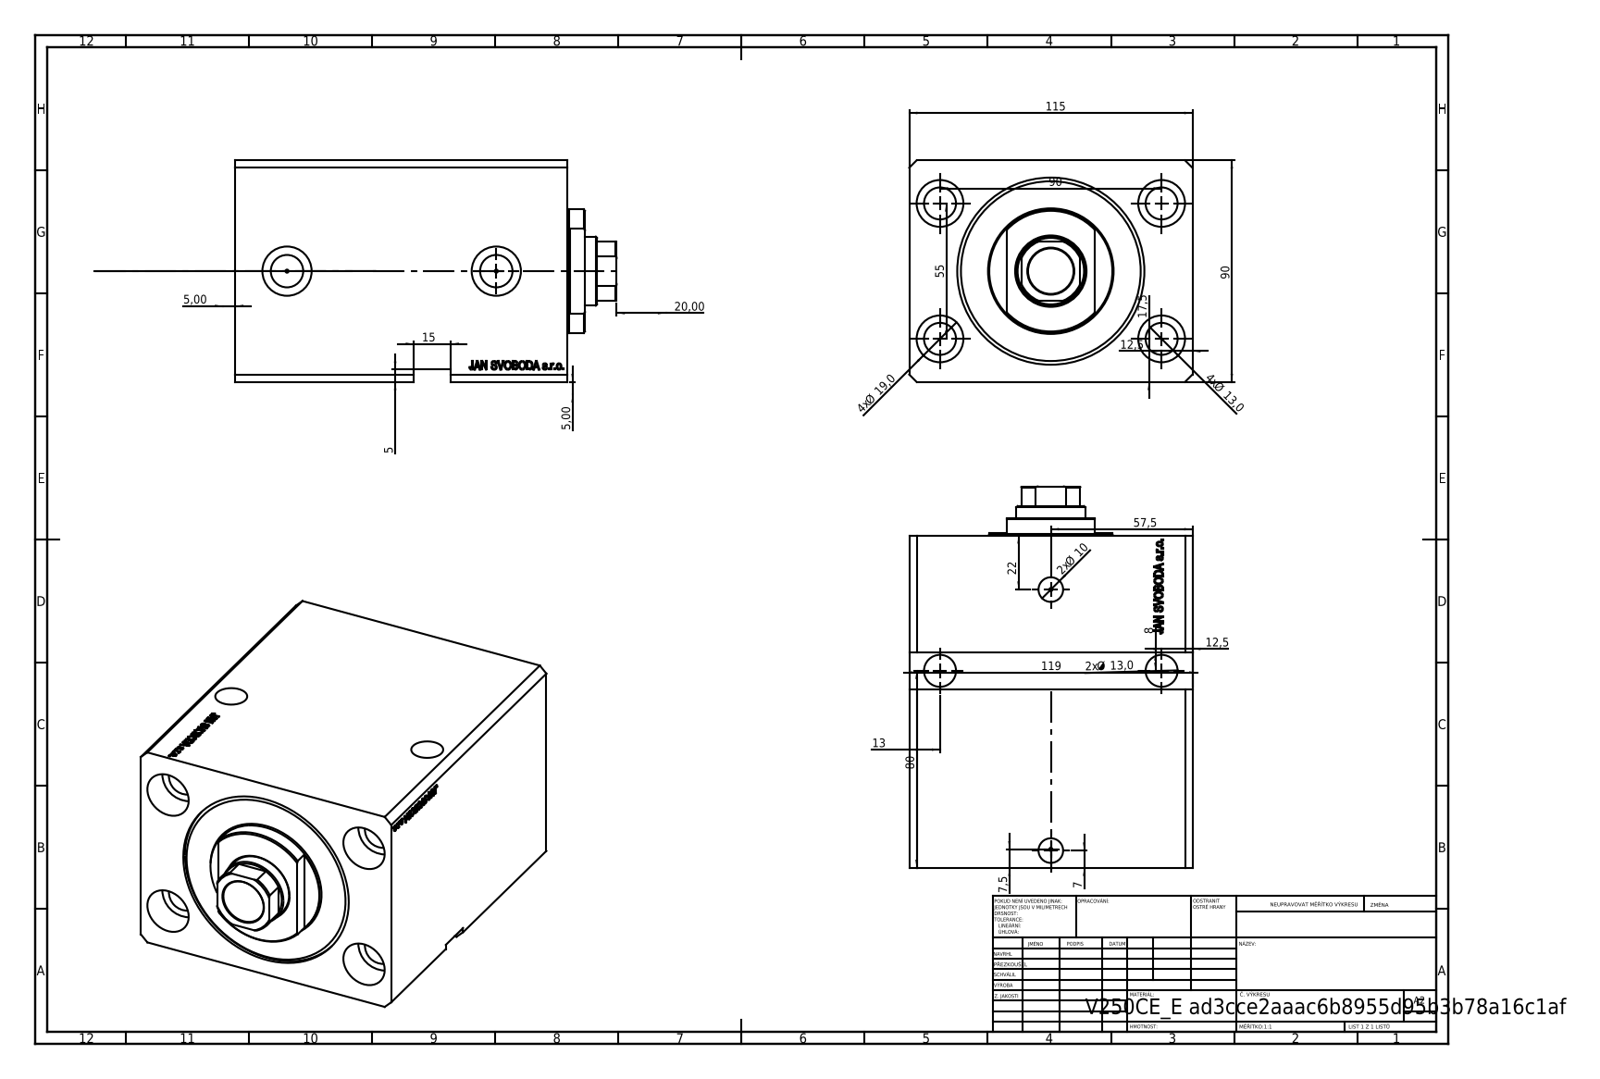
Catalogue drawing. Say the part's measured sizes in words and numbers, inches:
The part is named "V250CE_C_VCP; V250CE_E_Body; V250CE_VC_E". Its 3-D file was written by "SolidWorks 2019 (CONFIG_CONTROL_DESIGN)". It is 3 solids with 937 faces: 467 planar, 84 cylindrical and 386 other. Overall it measures 6.098 by 4.528 by 3.543 inches. Its volume is 70.91 cubic inches and its surface area 267.1 square inches. Round holes: 6 of diameter 0.512, 4 of diameter 0.049, 4 of diameter 0.748, 2 of diameter 0.394, 2 of diameter 0.518, 2 of diameter 0.787, 1 of diameter 0.728, 1 of diameter 1.102, 1 of diameter 2.48, 1 of diameter 2.992. Round bosses or shafts: 1 of diameter 1.969. Partial cylindrical surfaces (rounded edges, fillets, slot ends): 1 of radius 0.531. The main face-to-face distances are 3.543, 4.528, 5.315, 0.705, 4.61, 3.425, 4.13, 1.185, 1.969, 2.161. The hole center spacings are 2.076, 3.543, 2.165, 2.197, 3.358, 3.376, 4.153, 0.021.
